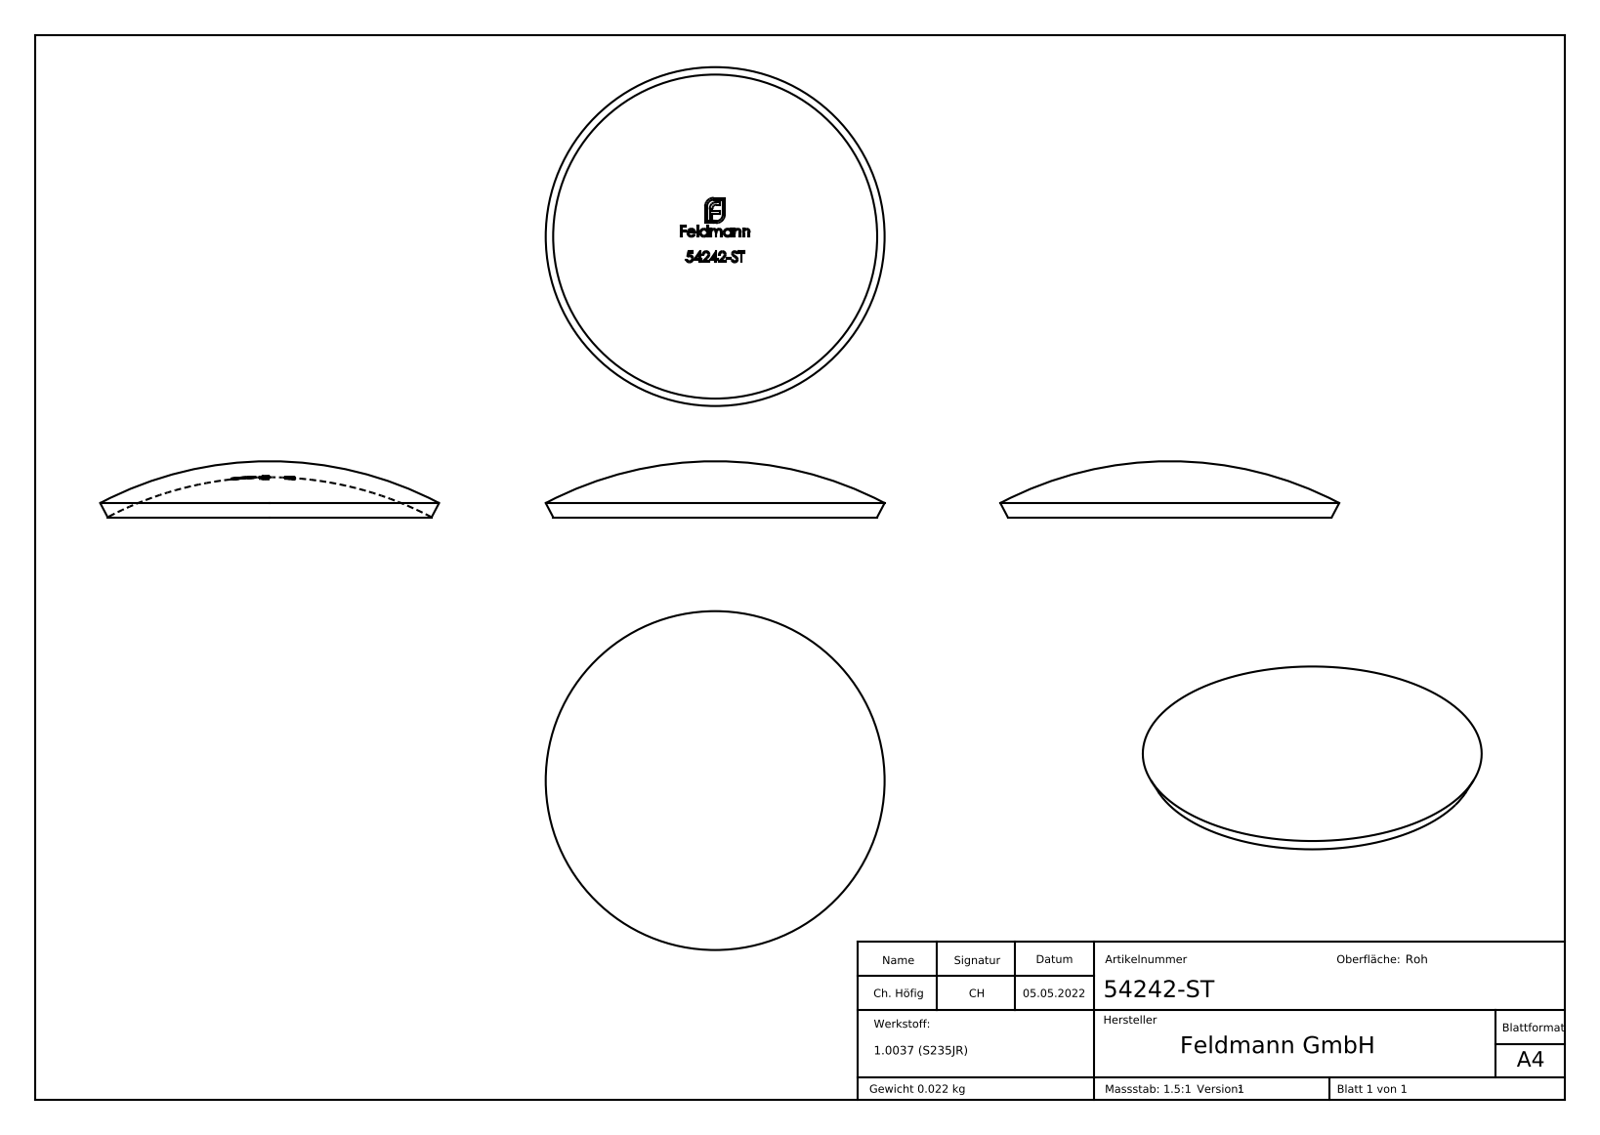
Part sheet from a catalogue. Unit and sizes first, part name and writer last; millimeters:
Units: millimetres
Overall size (bounding box): 42.4 × 42.4 × 7
Main face-to-face distances: 4.23, 3.19, 2.2, 1.26, 1.14, 0.99, 1.19, 0.63, 0.58, 0.34
Volume: 2 865 mm³ · Surface area: 3 139 mm²
Bodies: 1 solid, 262 faces (134 planar, 0 cylindrical, 128 other)
Part name (STEP PRODUCT): 54242-ST
STEP written by: SolidWorks 2018 (CONFIG_CONTROL_DESIGN)
